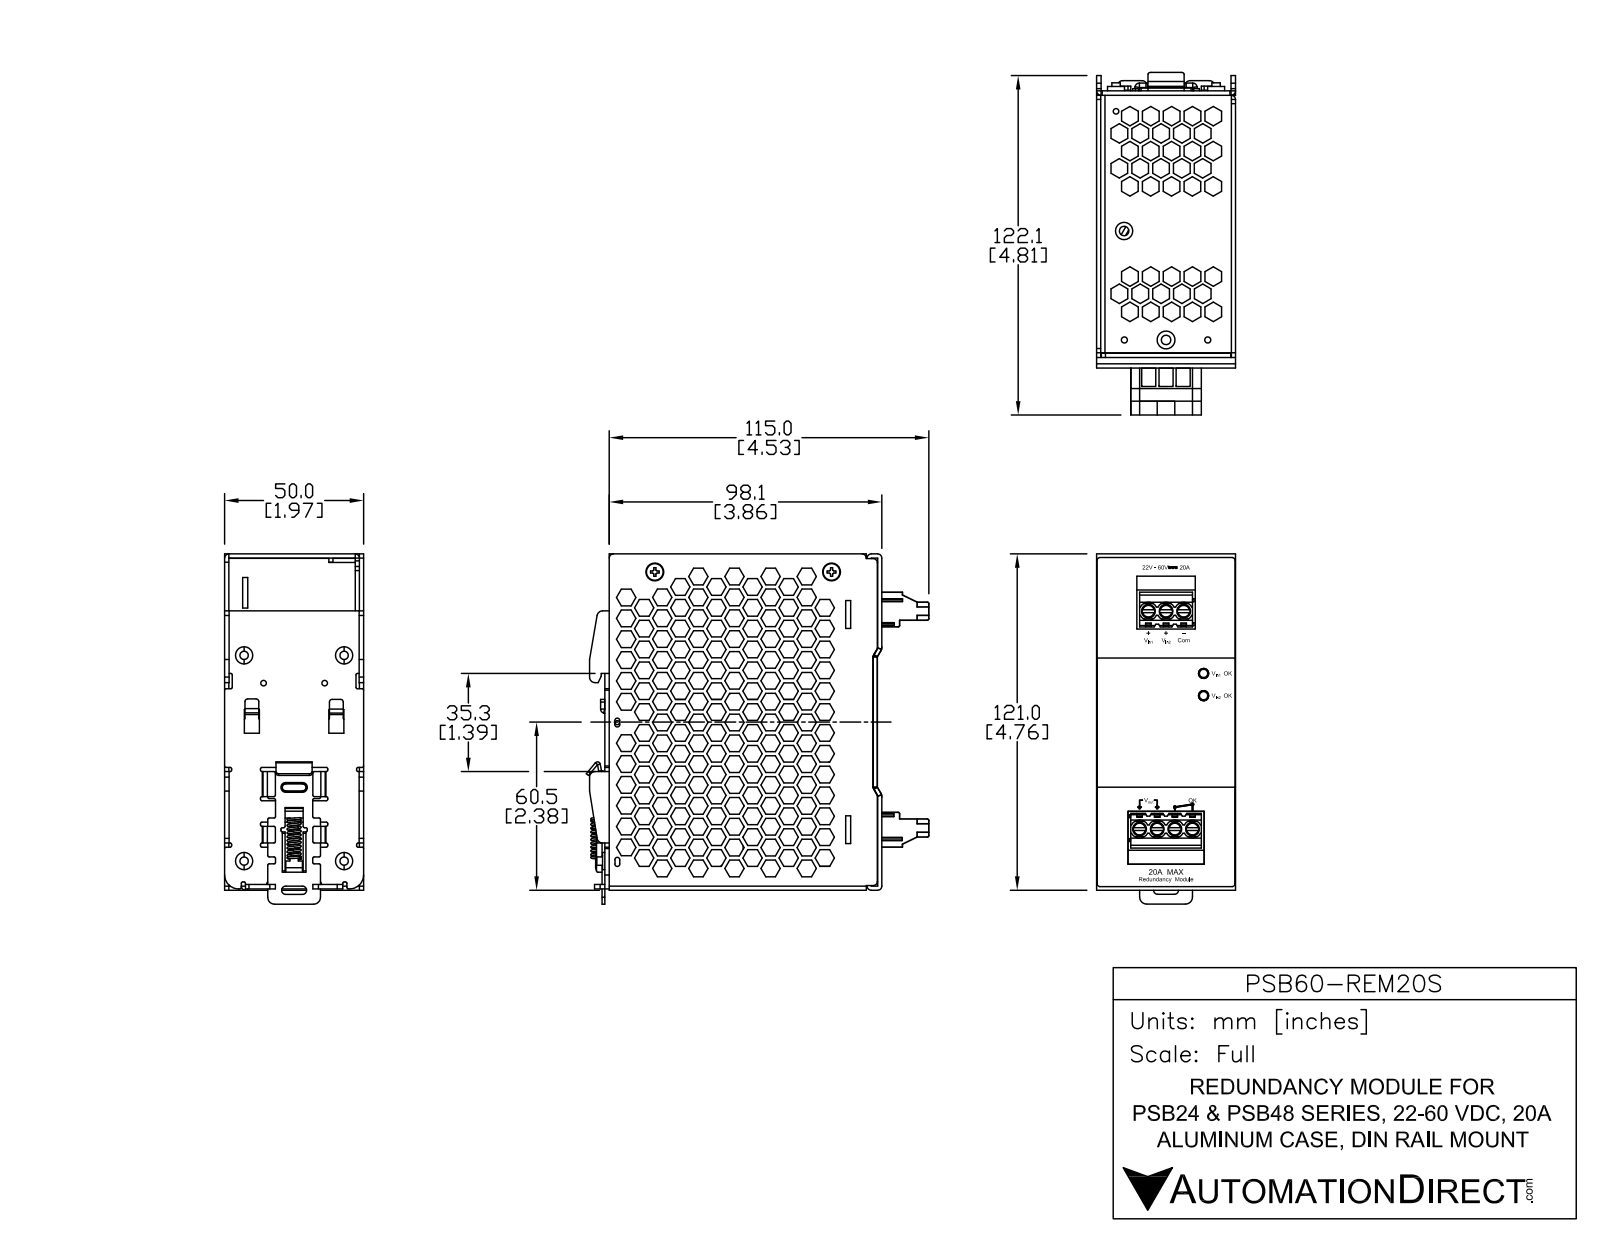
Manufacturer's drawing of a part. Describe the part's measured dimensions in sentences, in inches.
The part is named "330306690101_1; 3073461946_1; 3100000800_1; 3073461846_1 (+8 more)". Its 3-D file was written by "SolidWorks 2014 (AUTOMOTIVE_DESIGN)". It is 31 solids with 4284 faces: 3160 planar, 600 cylindrical and 524 other. Overall it measures 4.961 by 4.852 by 2.132 inches. Its volume is 4.928 cubic inches and its surface area 196.6 square inches. Round holes: 8 of diameter 0.157, 7 of diameter 0.077, 7 of diameter 0.083, 7 of diameter 0.181, 7 of diameter 0.193, 4 of diameter 0.087, 4 of diameter 0.098, 4 of diameter 0.118, 3 of diameter 0.079, 2 of diameter 0.138, 1 of diameter 0.13, 1 of diameter 0.299. Round bosses or shafts: 9 of diameter 0.236, 7 of diameter 0.187, 7 of diameter 0.118, 4 of diameter 0.205, 4 of diameter 0.106, 2 of diameter 0.276, 1 of diameter 0.315, 1 of diameter 0.299. Partial cylindrical surfaces (rounded edges, fillets, slot ends): 112 of radius 0.02, 36 of radius 0.059, 19 of radius 0.039, 18 of radius 0.079, 12 of radius 0.004, 9 of radius 0.063, 7 of radius 0.128, 6 of radius 0.01. The main face-to-face distances are 0.059, 0.063, 1.909, 3.618, 3.799, 0.122, 1.85, 1.969, 4.705, 3.681. The hole center spacings are 3.032, 3.053, 0.041, 0.25, 0.5, 2.991, 3.094, 3.569.
